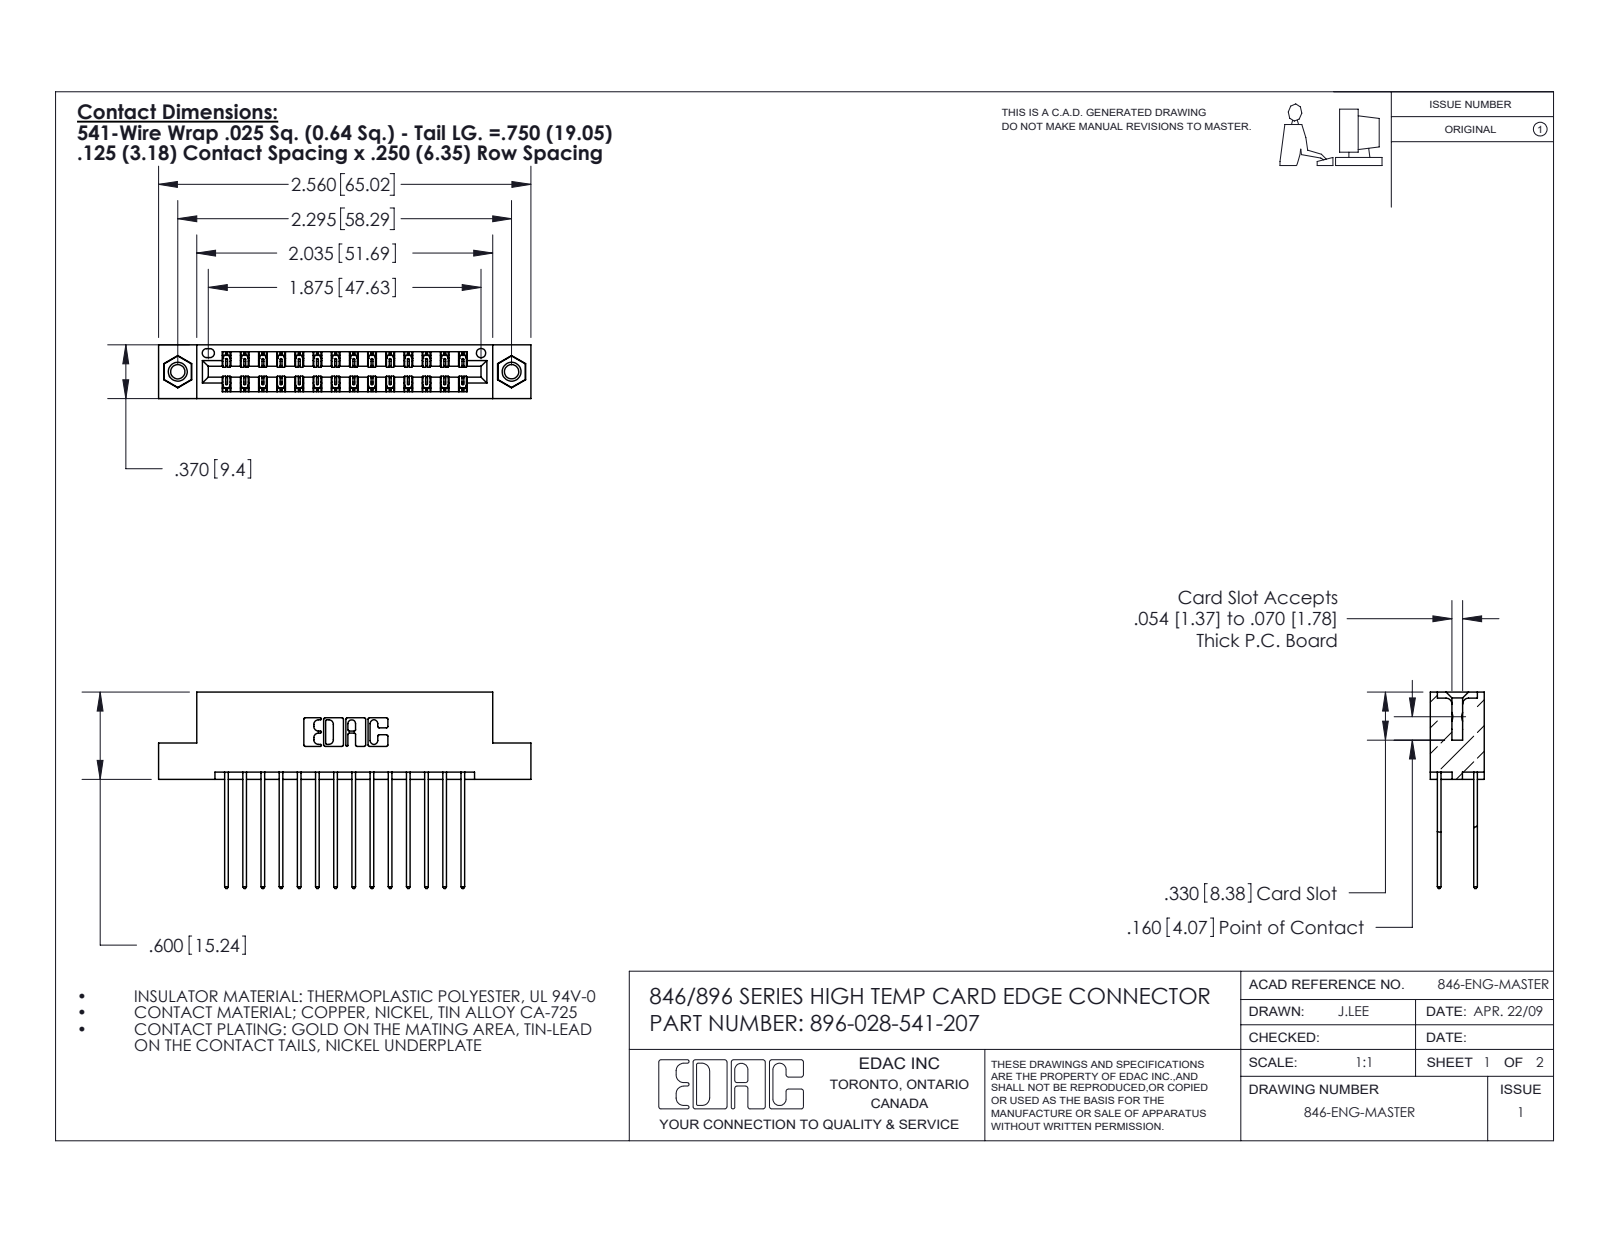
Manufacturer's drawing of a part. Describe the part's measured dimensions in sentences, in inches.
The part is named "345-292-001_345-293-141; 396-028-541-207; 345-250-001_345-250-005-103; 346 Part_Flush Mounting Lugs - 0.156 Dia-TI". Its 3-D file was written by "SolidWorks 2016 (CONFIG_CONTROL_DESIGN)". It is 31 solids with 1638 faces: 1088 planar, 534 cylindrical and 16 other. Overall it measures 2.56 by 1.35 by 0.37 inches. Its volume is 0.383 cubic inches and its surface area 13.92 square inches. Round holes: 2 of diameter 0.098, 2 of diameter 0.125, 2 of diameter 0.156, 1 of diameter 0.064. Round bosses or shafts: 2 of diameter 0.155. Partial cylindrical surfaces (rounded edges, fillets, slot ends): 42 of radius 0.006, 28 of radius 0.01, 22 of radius 0.01, 6 of radius 0.007, 6 of radius 0.031, 3 of radius 0.026, 2 of radius 0.014, 2 of radius 0.022. The main face-to-face distances are 0.048, 0.322, 0.25, 0.072, 0.298, 0.025, 0.37, 0.275, 0.148, 0.222. The hole center spacings are 0.246, 2.089, 2.295.
